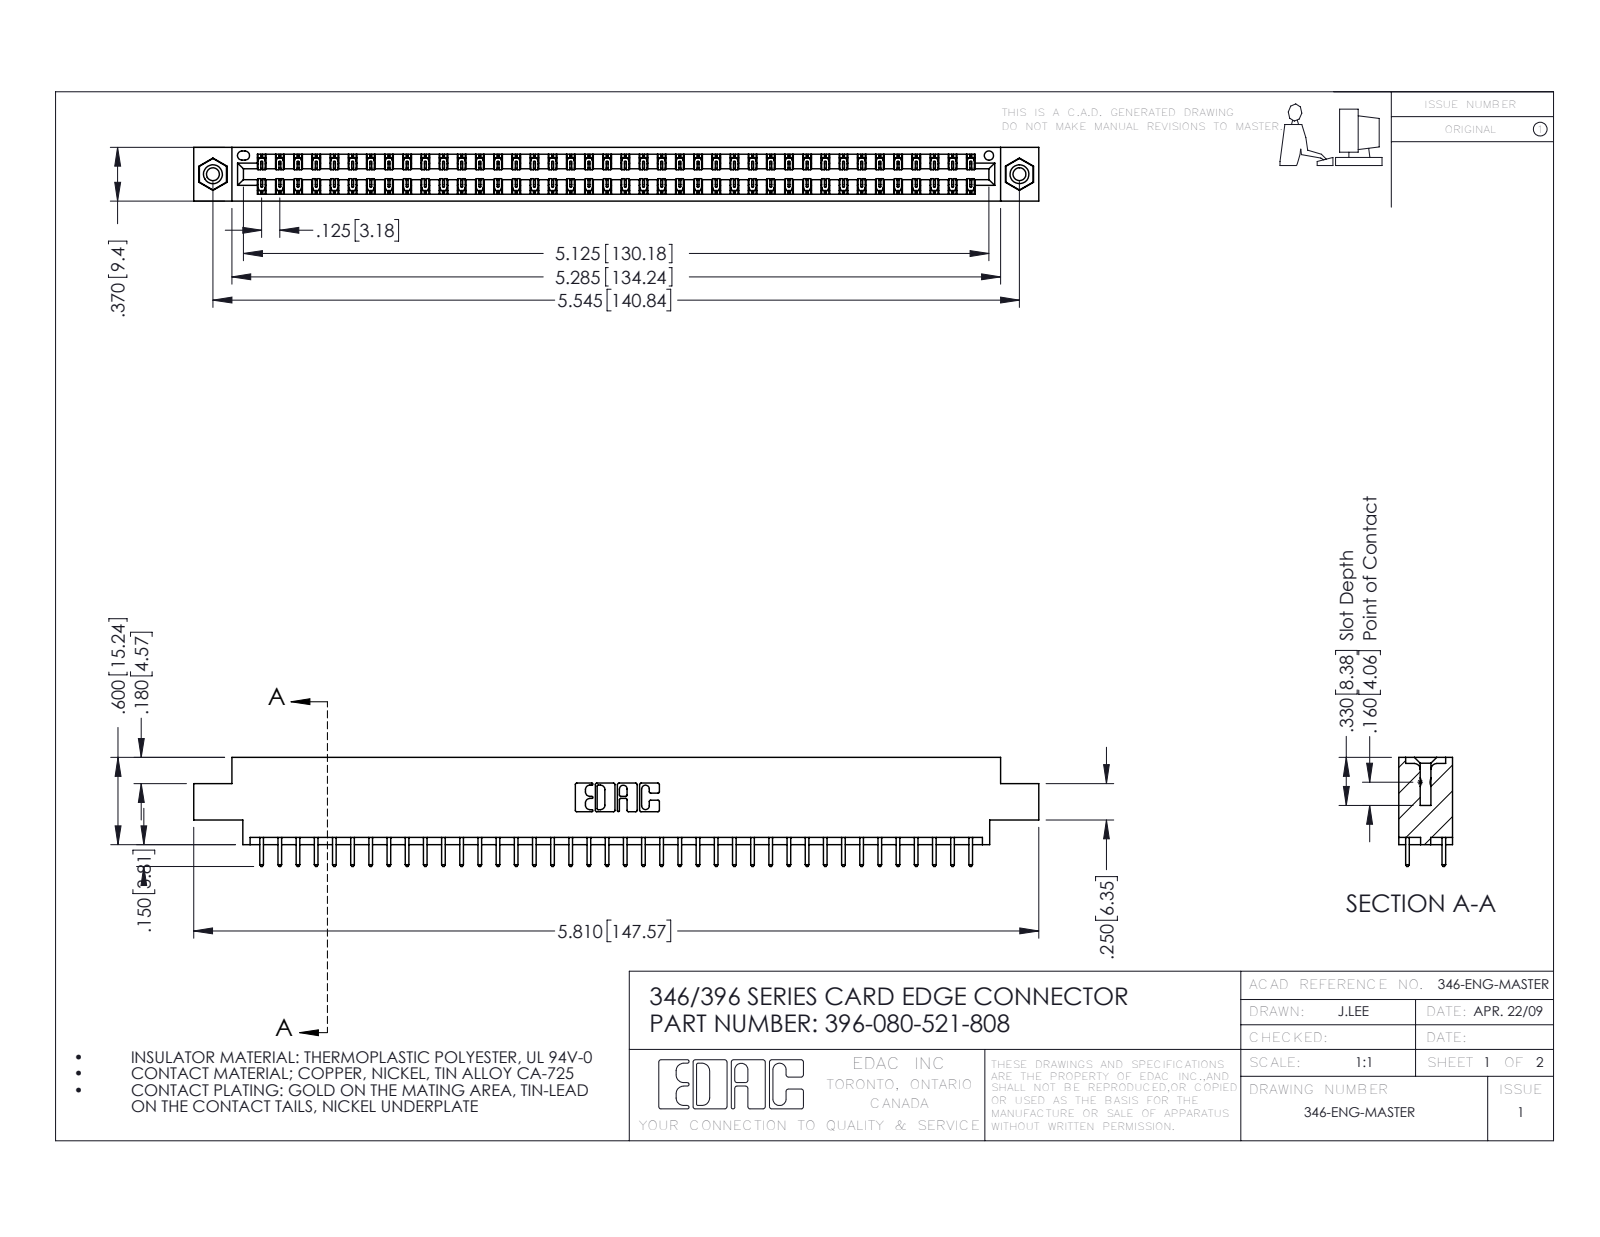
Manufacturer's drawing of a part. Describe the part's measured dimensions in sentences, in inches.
The part is named "396-080-521-808; 346 Part_0.170 Offset - 0.156 Dia-TI; 345-292-001_345-293-121; 345-250-001_345-250-003-102". Its 3-D file was written by "SolidWorks 2016 (CONFIG_CONTROL_DESIGN)". It is 83 solids with 4346 faces: 2912 planar, 1418 cylindrical and 16 other. Overall it measures 5.81 by 0.75 by 0.37 inches. Its volume is 0.865 cubic inches and its surface area 30.13 square inches. Round holes: 2 of diameter 0.089, 2 of diameter 0.125, 2 of diameter 0.156, 1 of diameter 0.064. Round bosses or shafts: 2 of diameter 0.155. Partial cylindrical surfaces (rounded edges, fillets, slot ends): 120 of radius 0.006, 80 of radius 0.01, 22 of radius 0.01, 6 of radius 0.007, 6 of radius 0.031, 3 of radius 0.026, 2 of radius 0.014, 2 of radius 0.022. The main face-to-face distances are 0.048, 0.322, 0.37, 0.25, 0.072, 0.298, 0.025, 0.275, 0.222, 0.148. The hole center spacings are 0.246, 5.336, 5.545.
